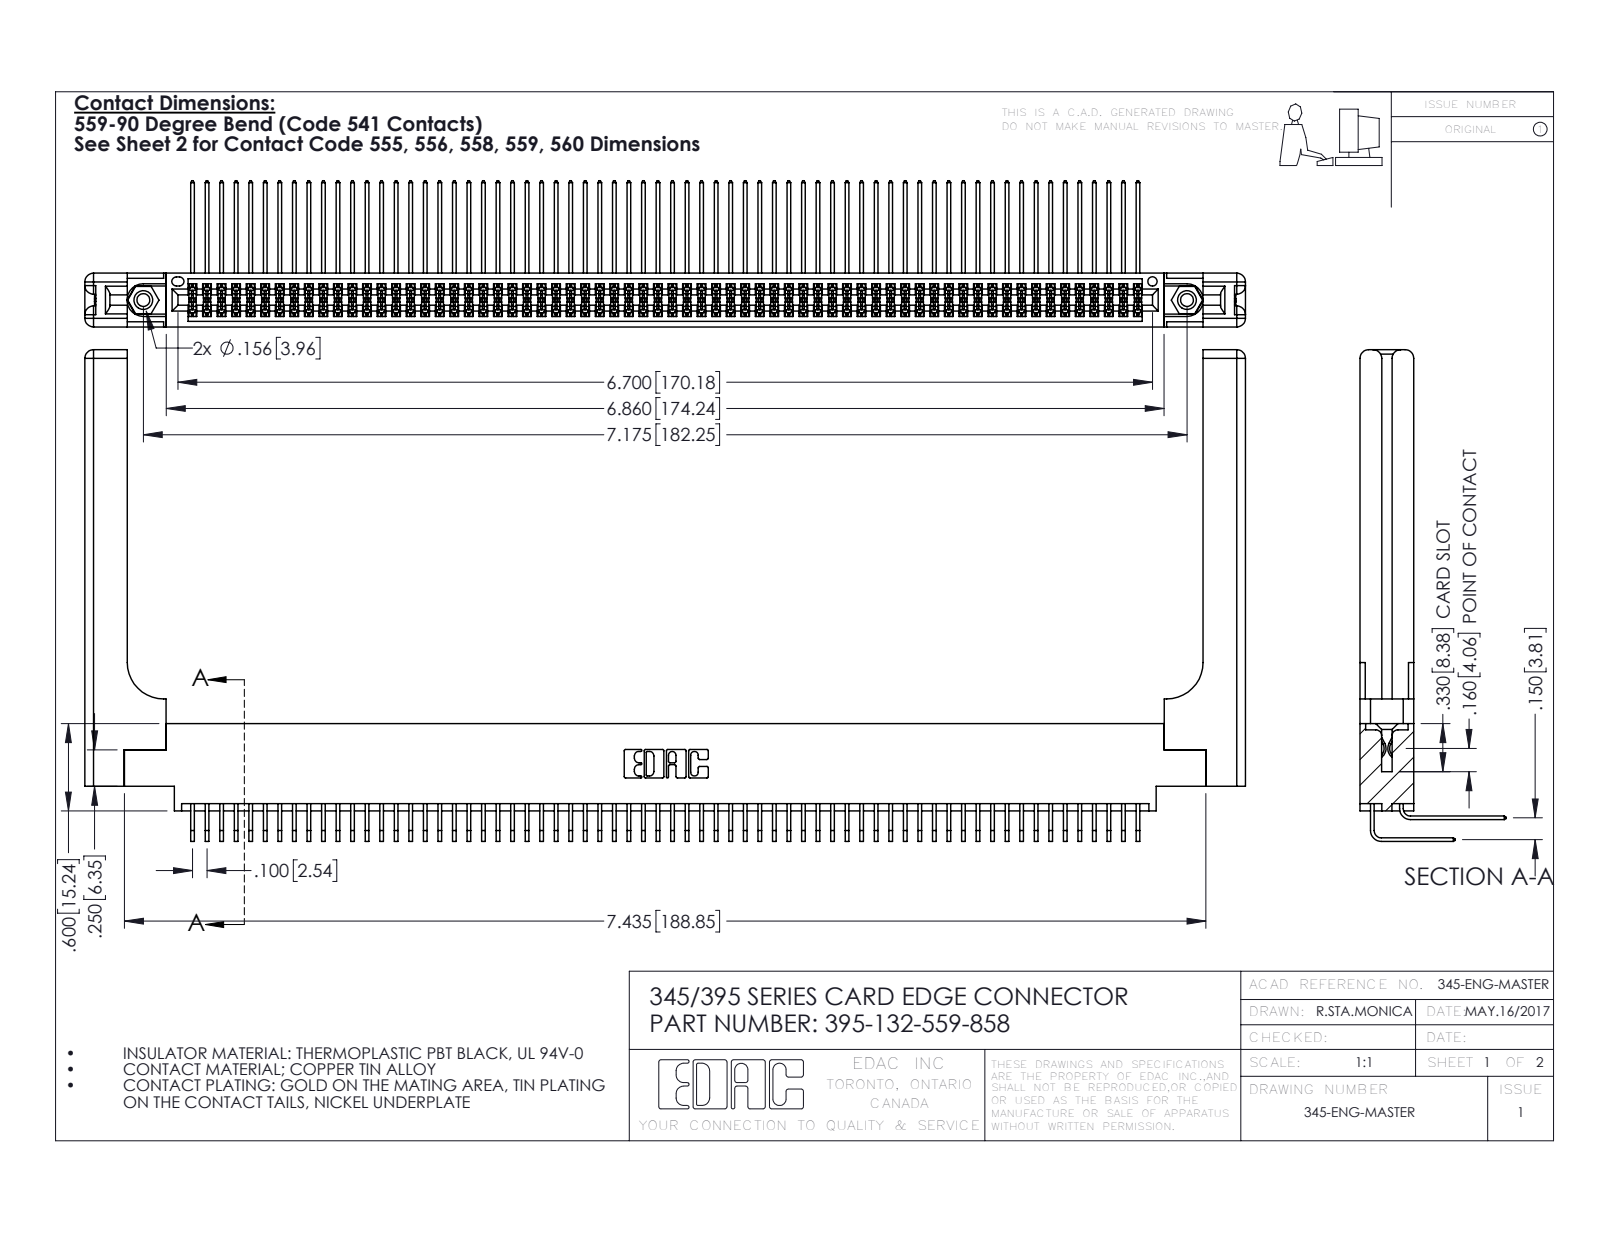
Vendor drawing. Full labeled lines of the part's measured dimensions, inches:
Part name (STEP PRODUCT): 345-220-058_345-220-058; 395-132-559-858; 345 Part_0.170 Offset - 0.156 Dia-TH; 345-250-001_345-250-001-102 (+2 more)
STEP written by: SolidWorks 2016 (CONFIG_CONTROL_DESIGN)
Units: inches
Bodies: 137 solids, 7250 faces (4852 planar, 2338 cylindrical, 60 other)
Overall size (bounding box): 7.979 × 3.379 × 1.005
Volume: 1.772 in³ · Surface area: 61.44 in²
Round holes (diameter × count): ⌀0.089 ×2, ⌀0.125 ×2, ⌀0.156 ×2, ⌀0.064 ×1
Round bosses / shafts (diameter × count): ⌀0.155 ×2
Partial cylindrical surfaces — rounded edges, fillets, slot ends (radius × count): R0.006 ×198, R0.01 ×22, R0.06 ×16, R0.007 ×6, R0.031 ×6, R0.026 ×3, R0.014 ×2, R0.019 ×2
Main face-to-face distances: 0.072, 0.298, 0.37, 0.098, 0.272, 0.025, 0.2, 0.225, 0.175, 0.15
Hole centre spacings: 0.27, 6.939, 7.175
